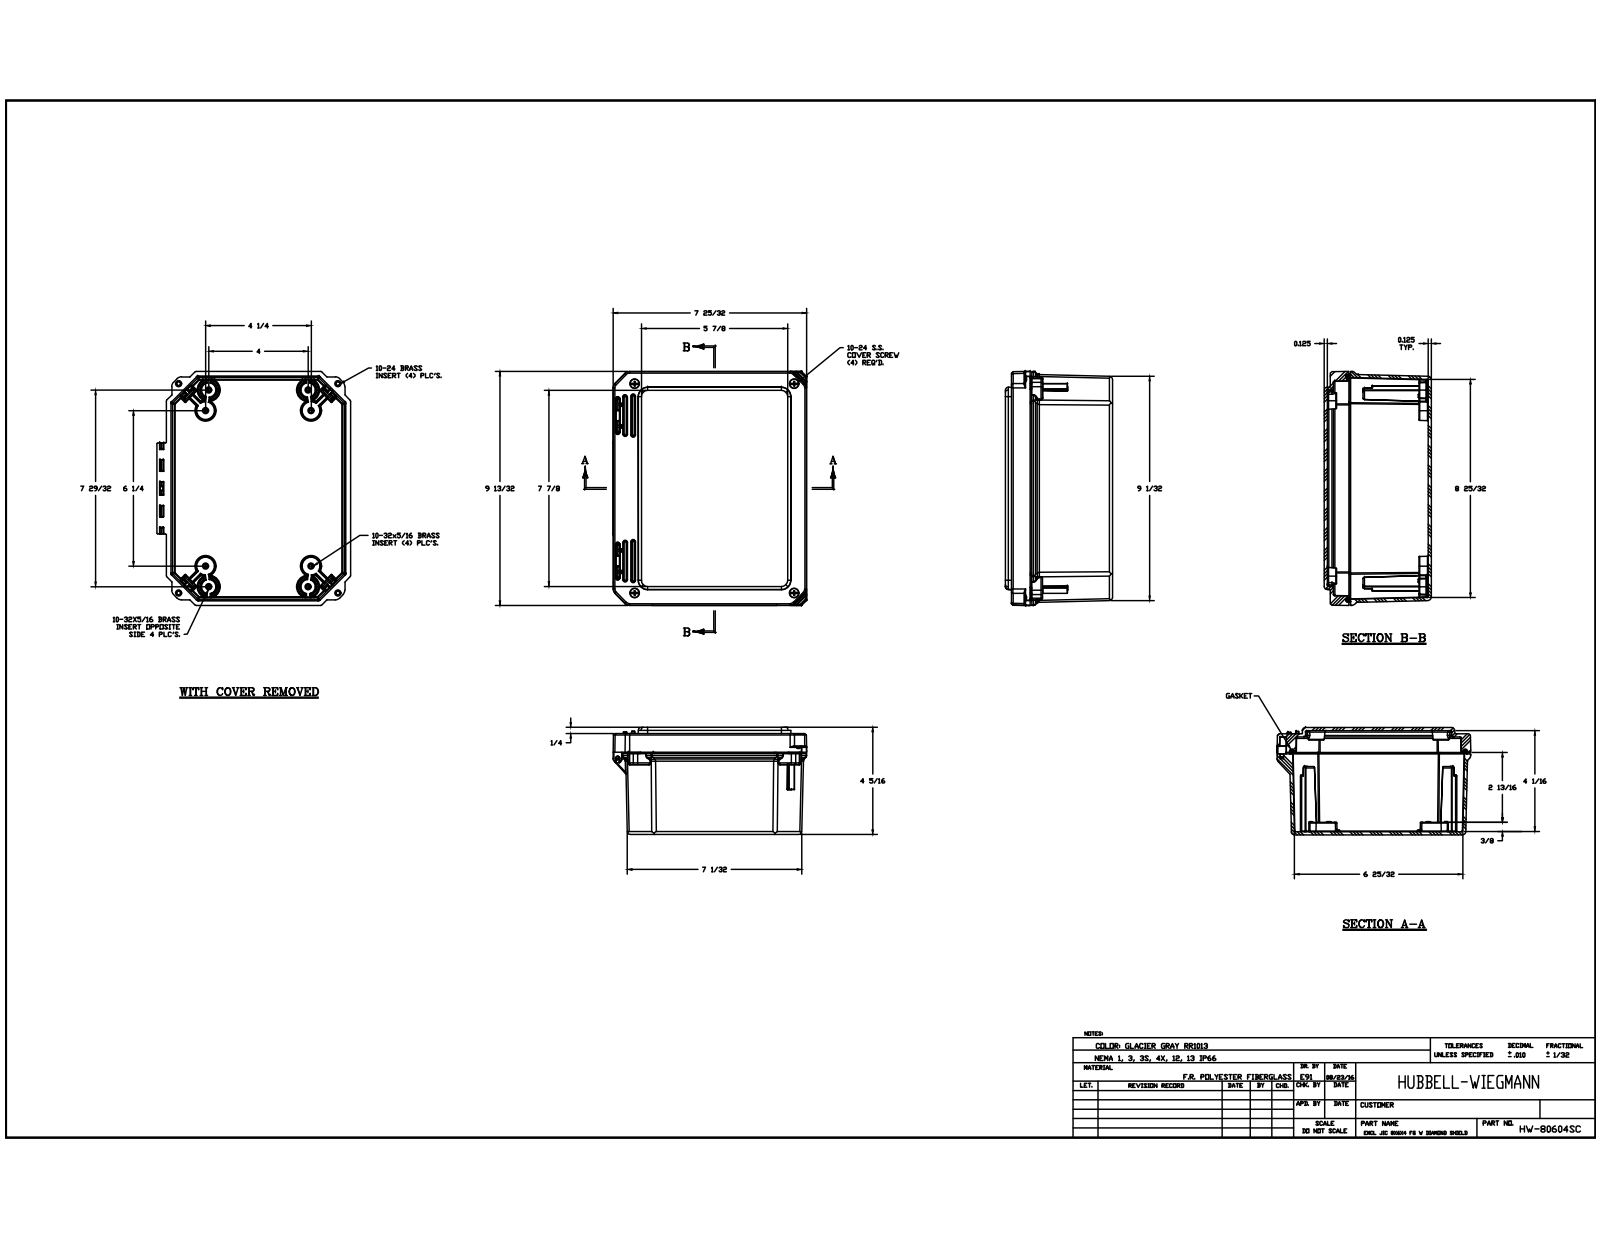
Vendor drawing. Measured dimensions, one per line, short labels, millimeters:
name: HW-80604SC; DS080604BOX; BRASS INSERT-(; BRASS INSERT-(_1 (+6 more)
written by: Autodesk Inventor 2017 (CONFIG_CONTROL_DESIGN)
unit: mm
bodies: 27 solids, 2018 faces (675 planar, 721 cylindrical, 622 other)
size: 239.6 × 197.87 × 109.48
volume: 726 198 mm³; area: 389 010 mm²
holes: 16× ⌀3.96, 8× ⌀3.86, 4× ⌀6.4, 4× ⌀6.43, 2× ⌀5.56, 2× ⌀5.77, 2× ⌀7.94, 1× ⌀3.48
bosses: 16× ⌀6.25, 4× ⌀22.1, 4× ⌀11.43, 4× ⌀5.05, 2× ⌀11.05
rounds: 104× R0.25, 80× R0.13, 65× R0.51, 42× R0.76, 27× R1.59, 24× R0.76, 24× R2.29, 24× R2.44
face distances: 3.17, 106.31, 109.48, 103.14, 6.35, 3.15, 99.96, 3.18, 103.13, 9.53
hole spacings: 208.09, 230.26, 38.85, 21.28, 31.3, 106.87, 107.95, 132.39
